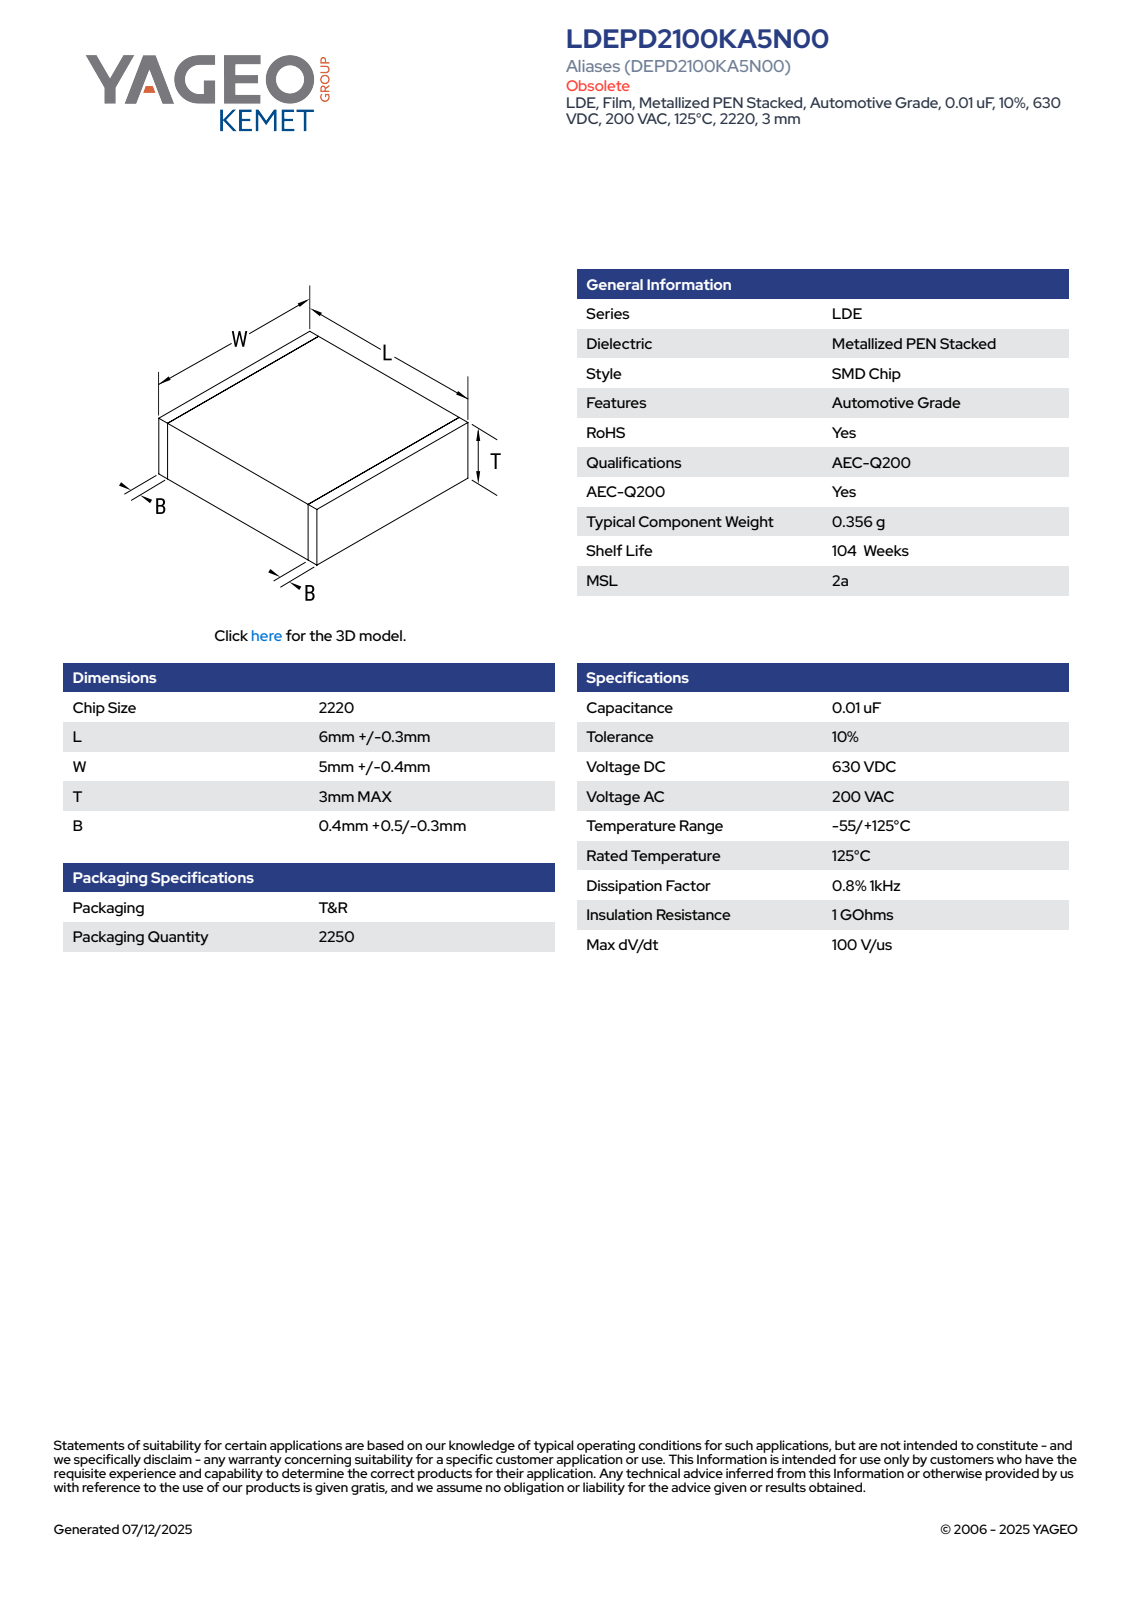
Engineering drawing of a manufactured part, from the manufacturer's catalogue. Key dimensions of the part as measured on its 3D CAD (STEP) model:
Part name (STEP PRODUCT): CFS_LDELDB_2220_L6.3W5.4T3B0.9
STEP written by: SolidWorks 2020 (AUTOMOTIVE_DESIGN)
Units: millimetres
Bodies: 4 solids, 73 faces (73 planar, 0 cylindrical, 0 other)
Overall size (bounding box): 6.3 × 5.4 × 3
Volume: 101 mm³ · Surface area: 140 mm²
Main face-to-face distances: 2.98, 6.3, 5.38, 2.99, 5.39, 3, 5.4, 0.5, 5.8, 5.3
